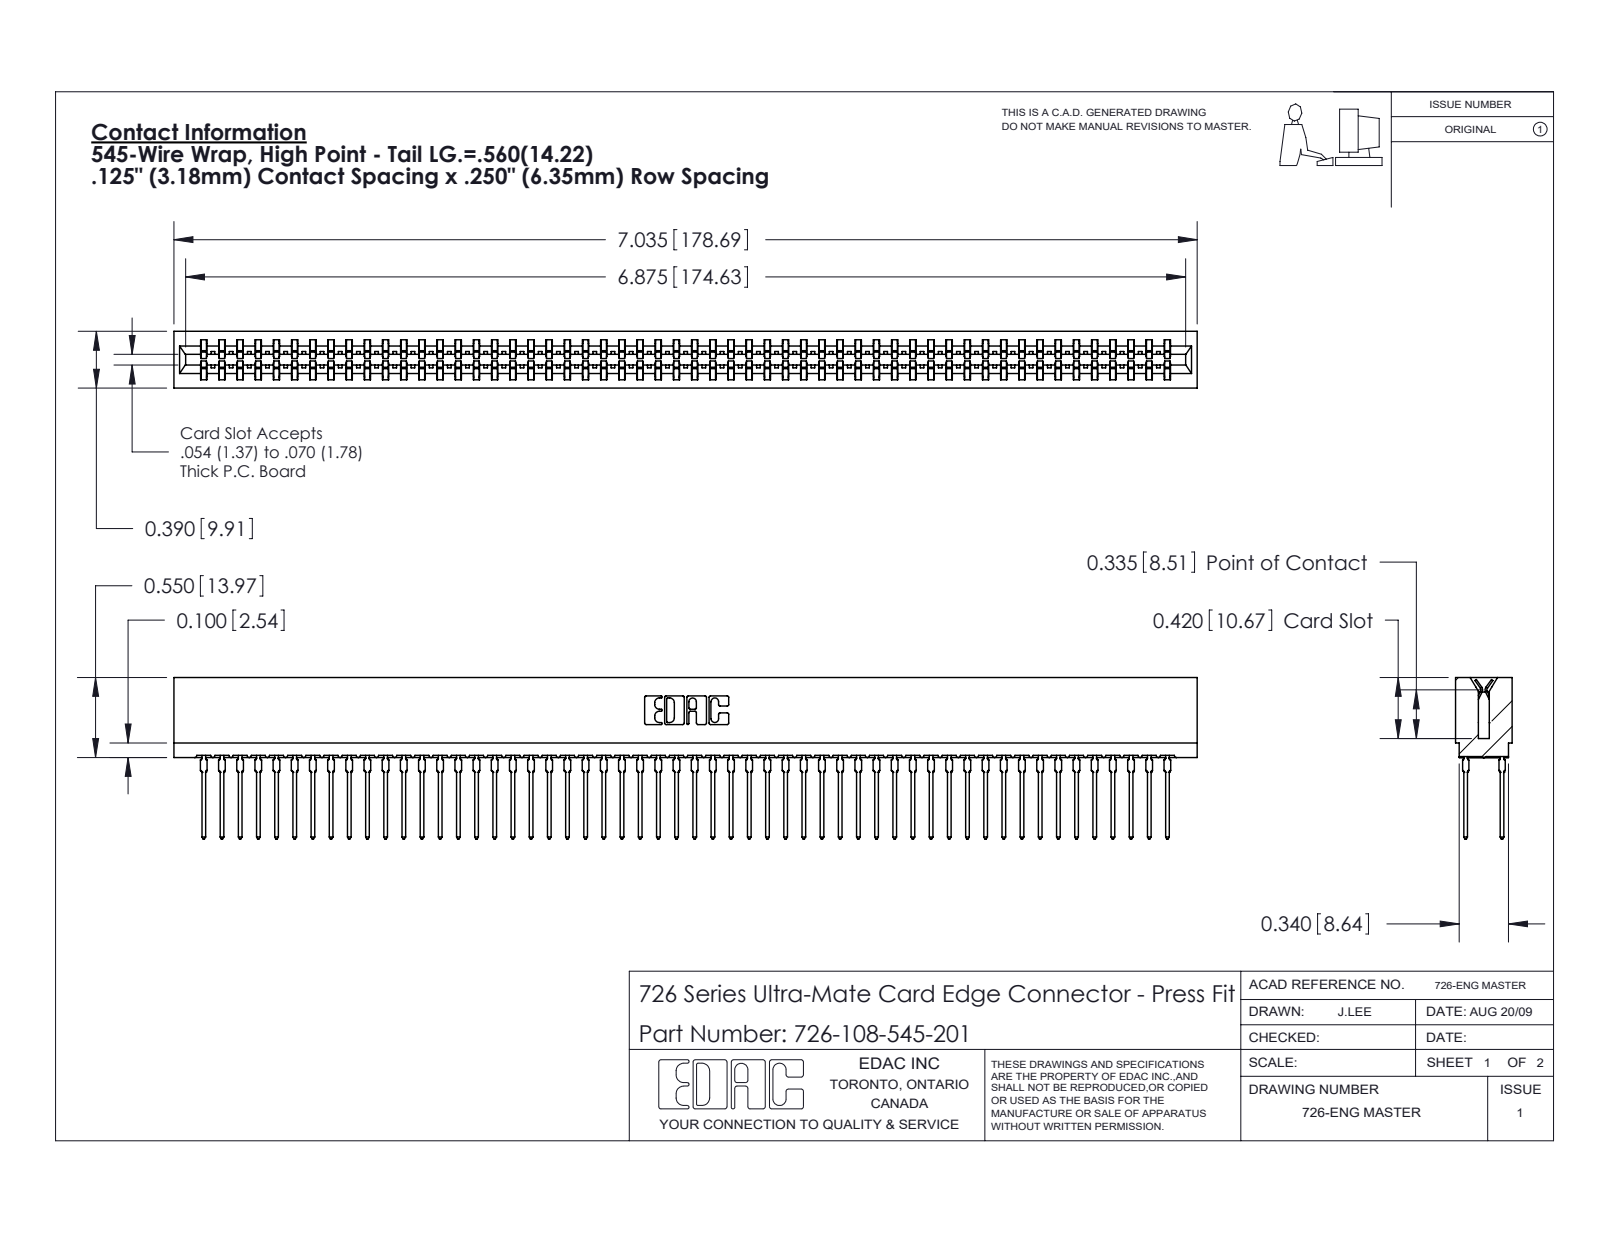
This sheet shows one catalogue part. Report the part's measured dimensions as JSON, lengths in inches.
{"part_name": "746-292-001_545; 726 Part_.515 Slot Depth - 01; 726-108-545-201", "step_written_by": "SolidWorks 2020 (CONFIG_CONTROL_DESIGN)", "units": "inches", "bodies": {"solids": 109, "faces": 9763, "planar": 5023, "cylindrical": 1932, "other": 2808}, "overall_size": [7.035, 1.109, 0.39], "volume_in3": 1.022, "surface_area_in2": 46.28, "partial_cylinders_radius": [[0.021, 216], [0.015, 55], [0.01, 22], [0.005, 8], [0.011, 8], [0.007, 6], [0.031, 6], [0.026, 3]], "face_to_face_distances": [0.057, 0.333, 0.025, 0.307, 0.39, 0.25, 0.275, 0.083, 0.365, 0.032]}
